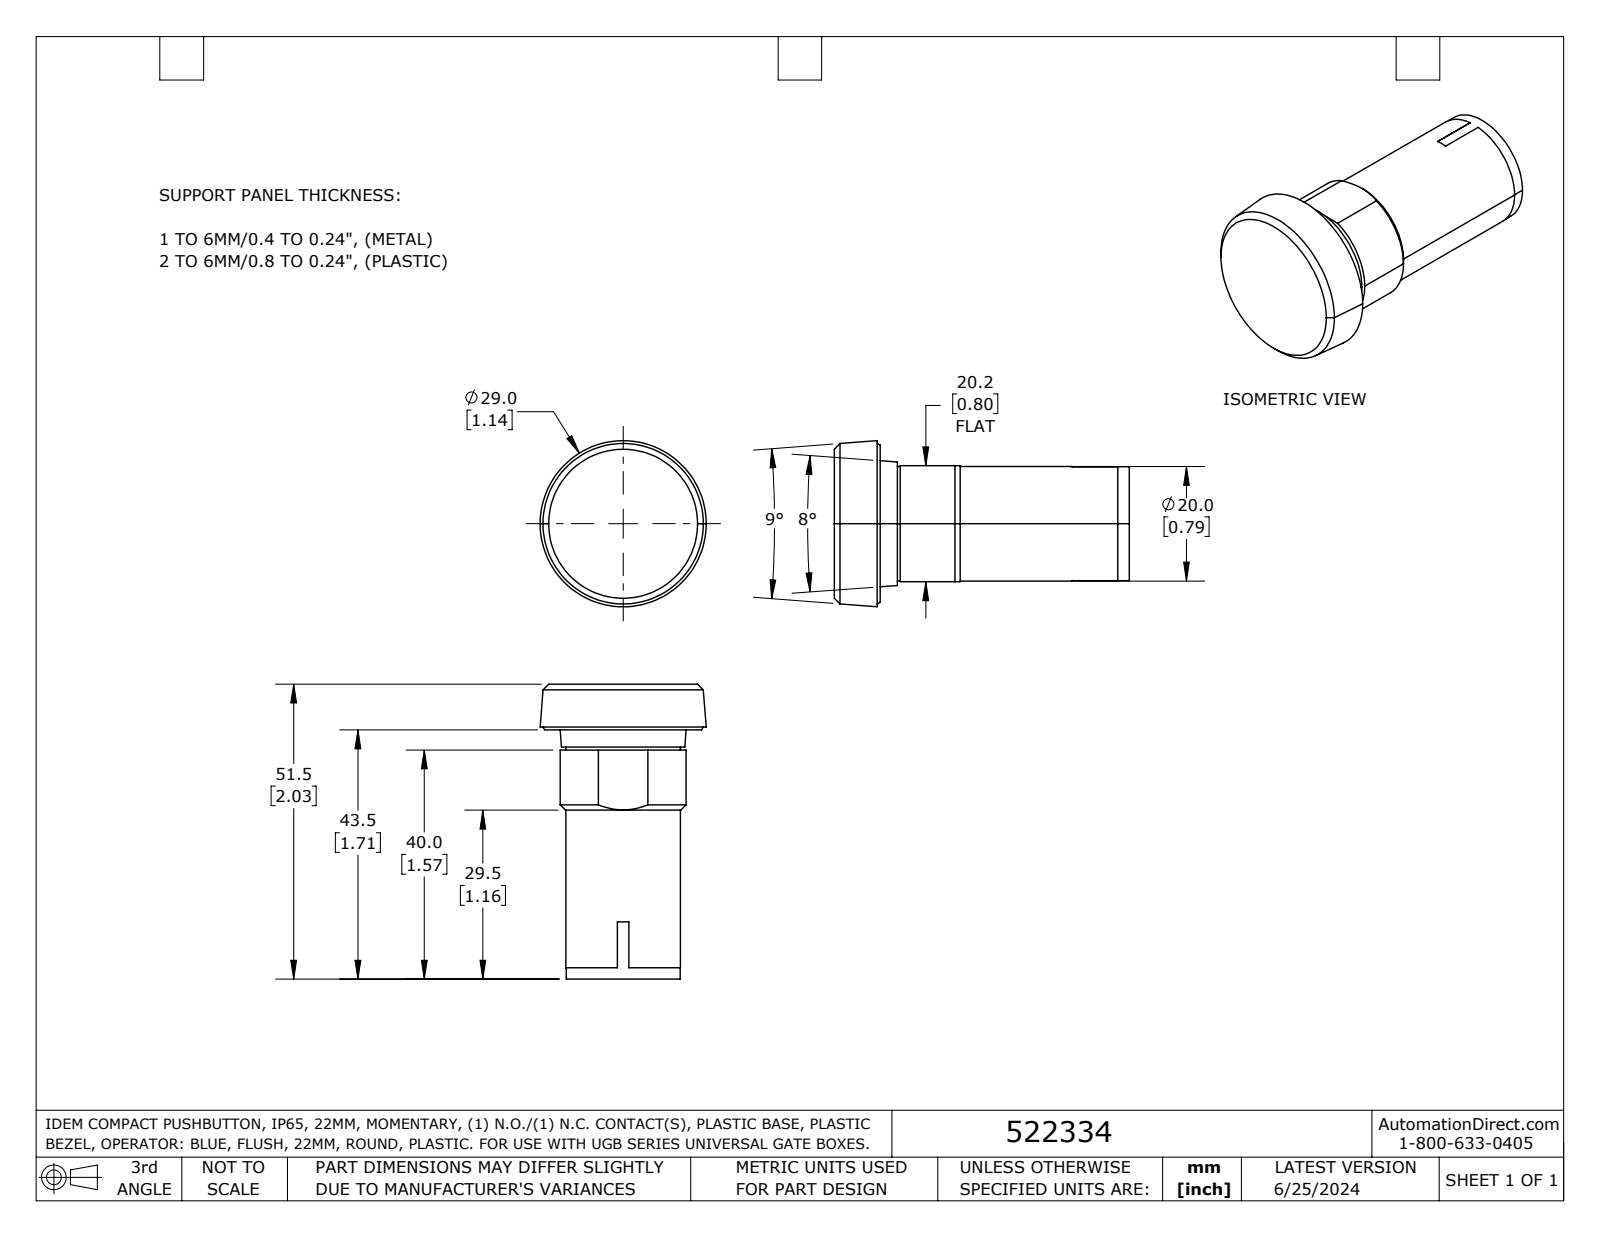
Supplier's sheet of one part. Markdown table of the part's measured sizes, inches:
| quantity | value |
| --- | --- |
| part name | 522334 |
| STEP written by | SolidWorks 2023 (AUTOMOTIVE_DESIGN) |
| units | inches |
| bodies | 1 solid, 37 faces (17 planar, 10 cylindrical, 10 other) |
| overall size | 2.028 × 1.142 × 1.142 |
| volume | 1.185 in³ |
| surface area | 7.436 in² |
| round bosses / shafts (diameter × count) | 0.787 × 1, 0.783 × 1 |
| partial cylindrical surfaces (radius × count) | 0.433 × 1 |
| main face-to-face distances | 2.028, 0.315, 1.713, 0.138, 0.02, 0.797, 0.433, 0.453, 1.575, 0.118 |
